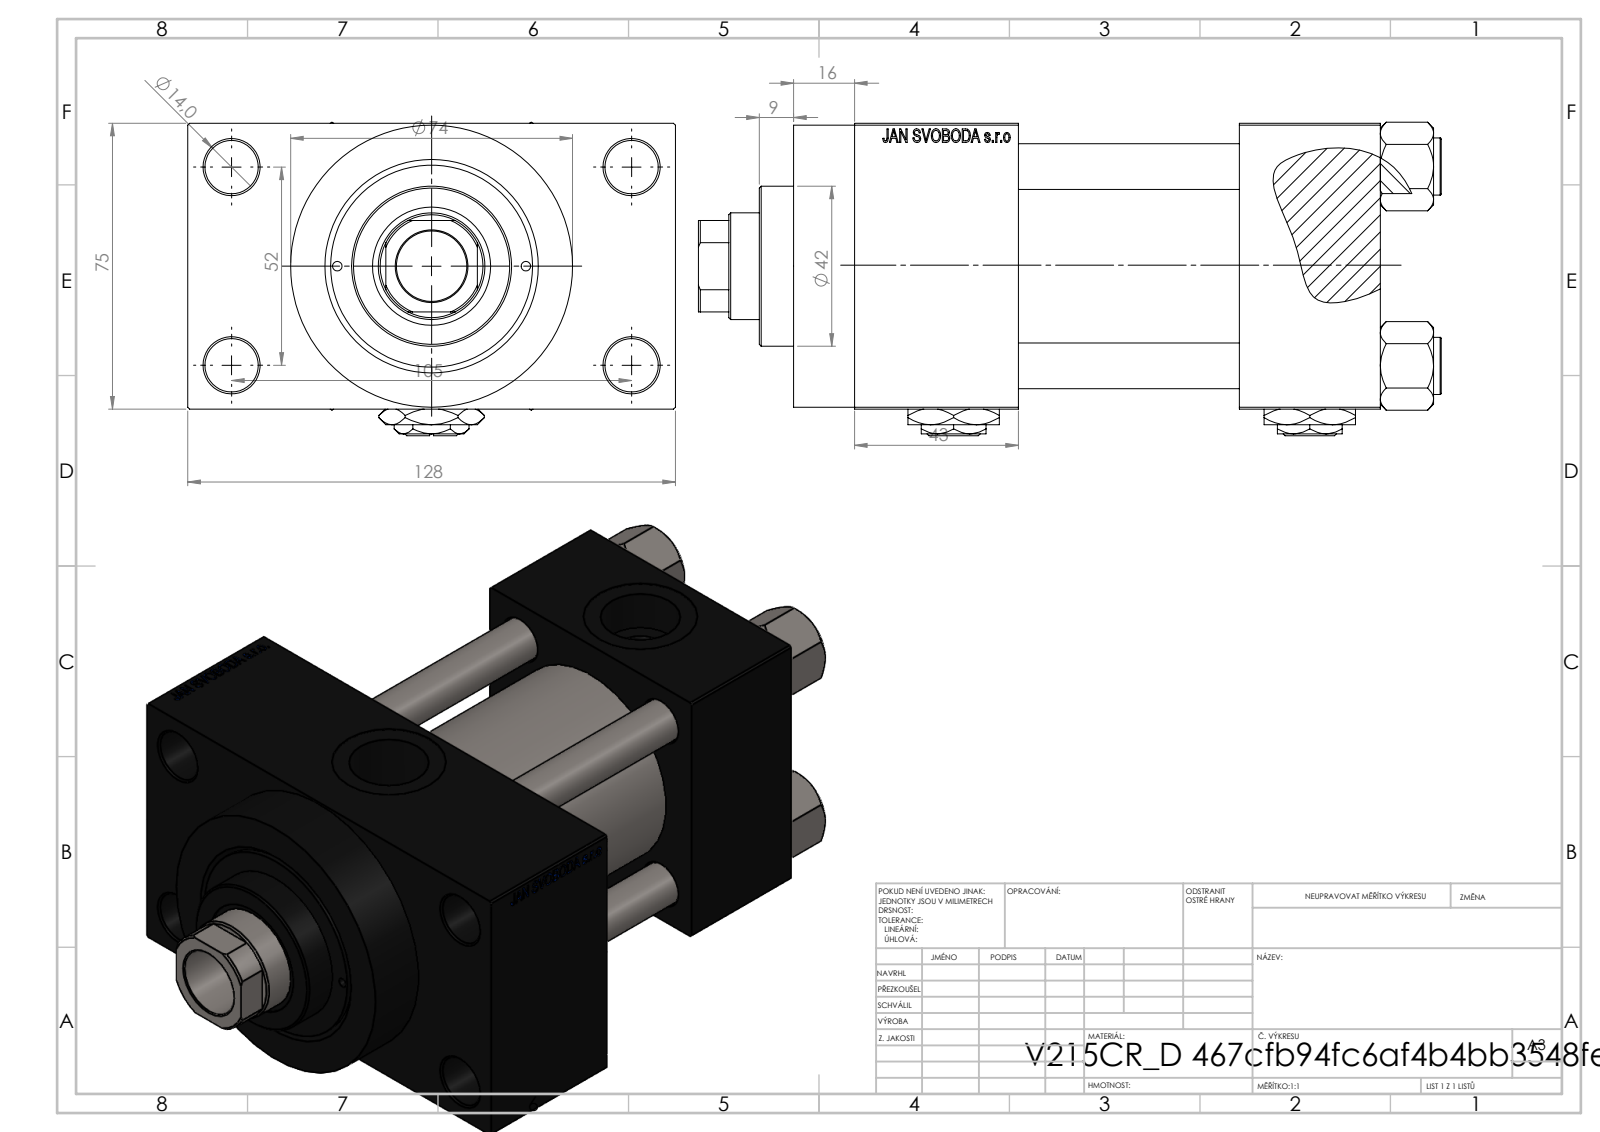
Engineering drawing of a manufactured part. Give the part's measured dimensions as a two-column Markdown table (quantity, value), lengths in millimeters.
| quantity | value |
| --- | --- |
| part name | V215CR_D_TYCINKA; Zatka_pro_OIL_PORT; V215CR_D_Body; V215_VC_A (+2 more) |
| STEP written by | SolidWorks 2019 (CONFIG_CONTROL_DESIGN) |
| units | millimeters |
| bodies | 13 solids, 1213 faces (547 planar, 104 cylindrical, 562 other) |
| overall size | 195 × 128 × 82.27 |
| volume | 810 628 mm³ |
| surface area | 173 039 mm² |
| round holes (diameter × count) | 12 × 4, 14 × 4, 2.5 × 2, 7 × 2, 20.96 × 2, 30 × 2, 18.5 × 1, 28 × 1, 31 × 1, 41 × 1, 50 × 1, 53 × 1 |
| round bosses / shafts (diameter × count) | 15 × 4, 74 × 1, 56 × 1, 42 × 1 |
| partial cylindrical surfaces (radius × count) | 13.5 × 1 |
| main face-to-face distances | 75, 58, 37, 95, 101.5, 26.5, 138, 101, 43, 16 |
| hole center spacings | 26.19, 26.35, 36.98, 38.03, 52.3, 57.22, 58.43, 58.59 |
